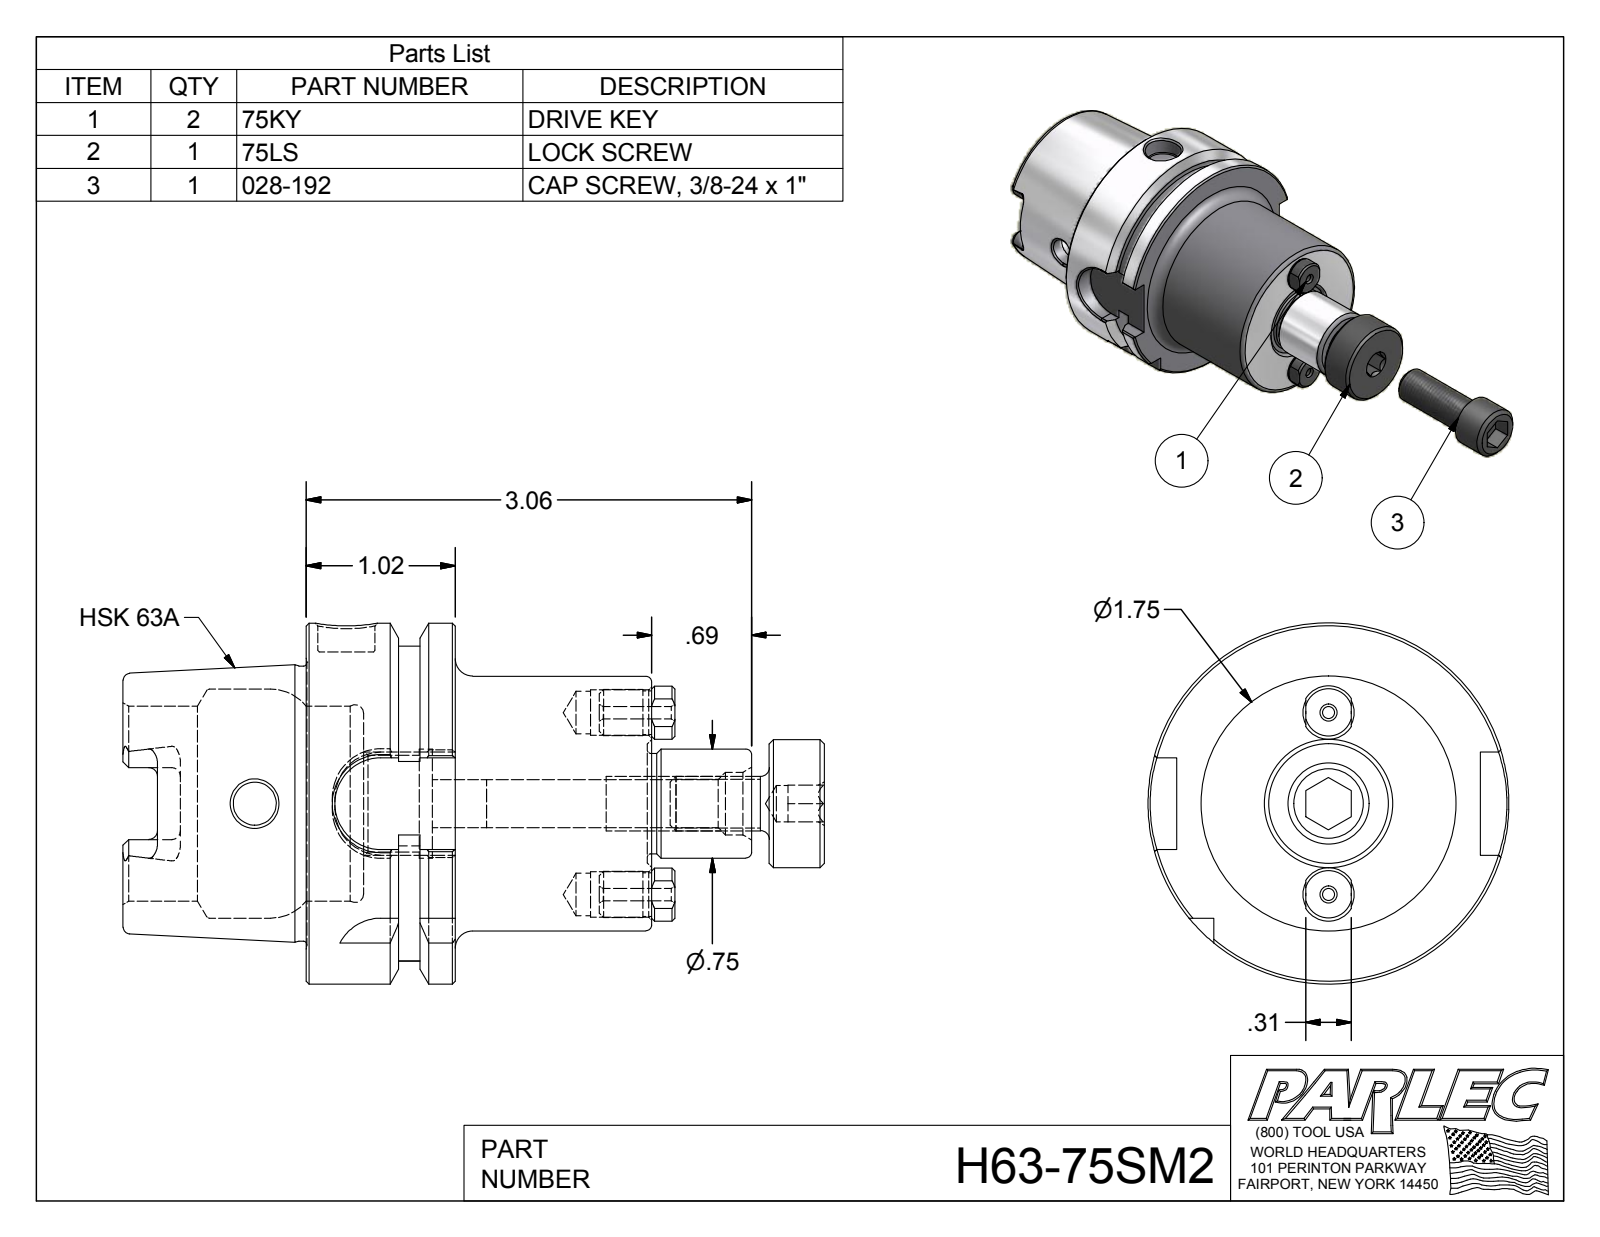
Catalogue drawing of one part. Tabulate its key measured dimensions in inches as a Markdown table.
| quantity | value |
| --- | --- |
| part name | H63-75SM2; 75KY; 75LS; 028-192 |
| STEP written by | Autodesk Inventor 2012 (AUTOMOTIVE_DESIGN) |
| units | inches |
| bodies | 5 solids, 222 faces (87 planar, 56 cylindrical, 79 other) |
| overall size | 6.694 × 2.48 × 2.48 |
| volume | 8.784 in³ |
| surface area | 54.1 in² |
| round holes (diameter × count) | 0.084 × 2, 0.292 × 2, 0.312 × 2, 0.25 × 1, 0.295 × 1, 0.33 × 1, 0.331 × 1, 0.394 × 1, 0.43 × 1, 0.666 × 1, 0.749 × 1, 1.339 × 1 |
| round bosses / shafts (diameter × count) | 0.318 × 2, 0.3 × 2, 2.48 × 1, 1.891 × 1, 1.75 × 1, 0.88 × 1, 0.75 × 1, 0.69 × 1 |
| partial cylindrical surfaces (radius × count) | 0.059 × 6, 0.113 × 4, 0.315 × 4, 0.183 × 2, 1.083 × 1 |
| main face-to-face distances | 1.024, 2.375, 1.352, 0.241, 0.389, 0.394, 0.63, 1.981, 1.26, 1.654 |
| hole center spacings | 0.625, 1.25 |
